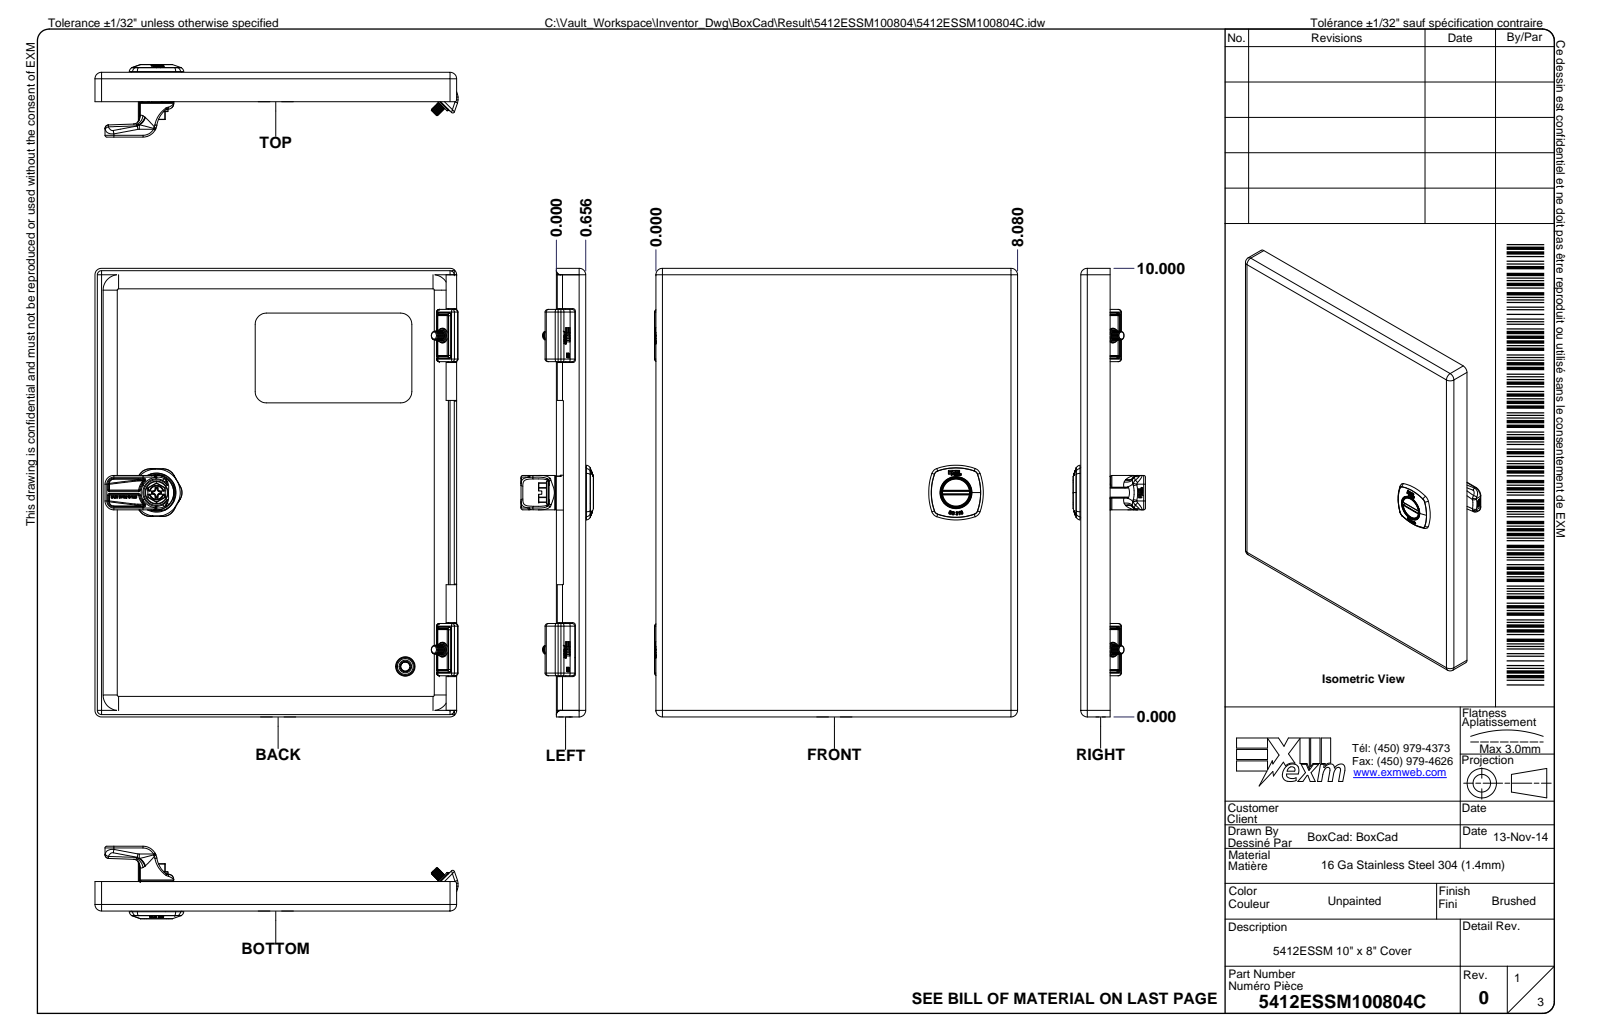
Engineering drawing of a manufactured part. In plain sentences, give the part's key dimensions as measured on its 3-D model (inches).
The part is named "5412ESSM100804; 5412ESSM100804B; 5412ESSM100804B-P; STK-Q-08500 (+8 more)". Its 3-D file was written by "Autodesk Inventor 2024 (AUTOMOTIVE_DESIGN)". It is 53 solids with 6783 faces: 3458 planar, 1207 cylindrical and 2118 other. Overall it measures 11.496 by 8.111 by 4.77 inches. Its volume is 26.18 cubic inches and its surface area 922.5 square inches. Round holes: 8 of diameter 0.201, 6 of diameter 0.03, 6 of diameter 0.24, 5 of diameter 0.311, 4 of diameter 0.197, 4 of diameter 0.32, 3 of diameter 0.236, 2 of diameter 0.165, 2 of diameter 0.173, 2 of diameter 0.181, 2 of diameter 0.218, 1 of diameter 0.127. Round bosses or shafts: 9 of diameter 0.232, 6 of diameter 0.394, 6 of diameter 0.035, 5 of diameter 0.512, 4 of diameter 0.5, 3 of diameter 0.197, 3 of diameter 0.193, 2 of diameter 0.3. Partial cylindrical surfaces (rounded edges, fillets, slot ends): 123 of radius 0.02, 114 of radius 0.008, 58 of radius 0.012, 55 of radius 0.01, 42 of radius 0.004, 38 of radius 0.039, 28 of radius 0.031, 24 of radius 0.079. The main face-to-face distances are 0.053, 4.428, 4.375, 4.481, 7.947, 4.035, 0.447, 0.394, 3.981, 0.461. The hole center spacings are 10.35, 0.546, 6.25, 7.11, 8.781, 10.706, 6.148, 8.25.
